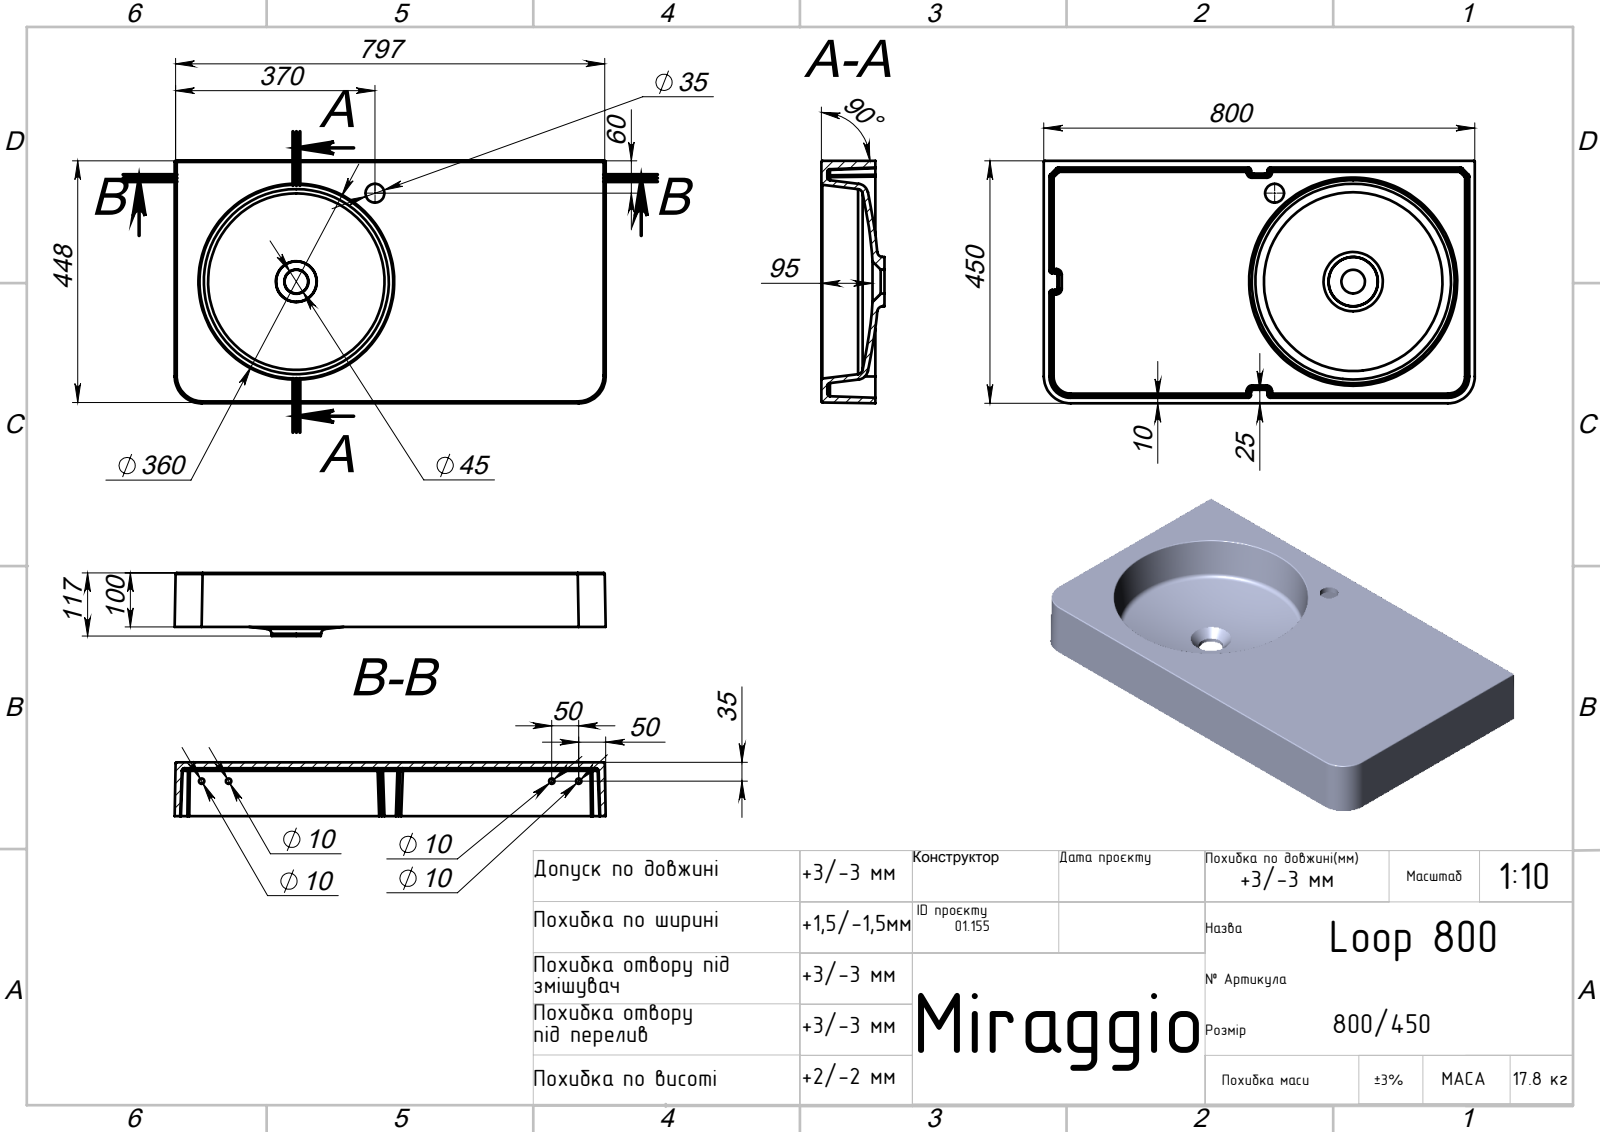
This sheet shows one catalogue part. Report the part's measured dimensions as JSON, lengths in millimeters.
{"part_name": "Loop 800", "step_written_by": "SolidWorks 2020 (AUTOMOTIVE_DESIGN)", "units": "millimeters", "bodies": {"solids": 1, "faces": 130, "planar": 29, "cylindrical": 55, "other": 46}, "overall_size": [800, 450, 117], "volume_mm3": 7123000, "surface_area_mm2": 1284000, "round_holes": [[10, 4], [35, 1]], "partial_cylinders_radius": [[5, 29], [2, 6], [22.5, 2], [50, 2]], "face_to_face_distances": [11, 89, 100, 27.5, 72.5, 17, 106, 117, 89.5, 16.5], "hole_center_spacings": [50, 650, 600, 700]}
